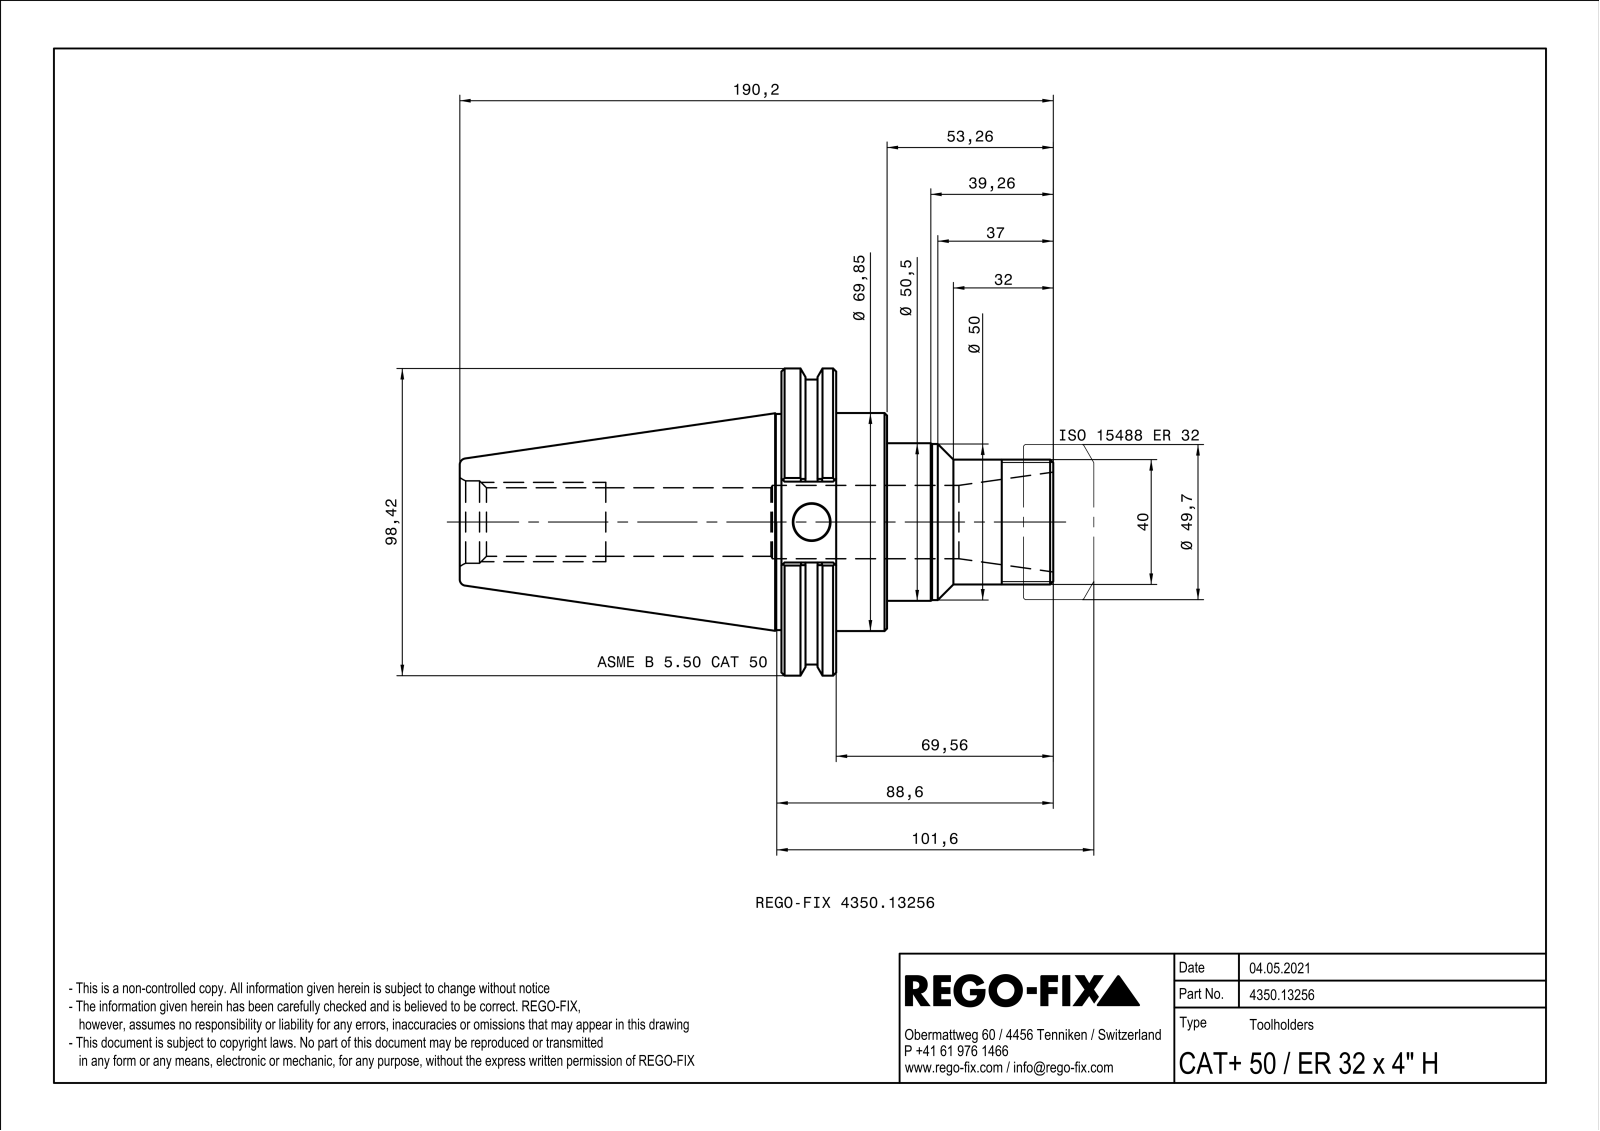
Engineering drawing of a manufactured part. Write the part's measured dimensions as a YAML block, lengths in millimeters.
part_name: "NOCUT"
step_written_by: "SIEMENS PLM Software Solid Edge ST10 (AUTOMOTIVE_DESIGN)"
units: millimeters
bodies: {solids: 2, faces: 249, planar: 102, cylindrical: 59, other: 88}
overall_size: [190.6, 98.72, 94.65]
volume: 865304
surface_area: 120708
round_holes:
  - {diameter: 3.9, count: 2}
  - {diameter: 4.5, count: 2}
  - {diameter: 3.24, count: 1}
  - {diameter: 12, count: 1}
  - {diameter: 21.96, count: 1}
  - {diameter: 23.5, count: 1}
  - {diameter: 26.1, count: 1}
  - {diameter: 26.4, count: 1}
round_bosses_or_shafts:
  - {diameter: 98.72, count: 1}
  - {diameter: 98.43, count: 1}
  - {diameter: 91.3, count: 1}
  - {diameter: 70.15, count: 1}
  - {diameter: 69.85, count: 1}
  - {diameter: 69.25, count: 1}
  - {diameter: 50.8, count: 1}
  - {diameter: 50.5, count: 1}
partial_cylinders:
  - {radius: 0.5, count: 4}
face_to_face_distances: [33.75, 17.55, 17.75, 16, 33.55, 16.2, 33.95, 136.85, 103.1, 72.73]
